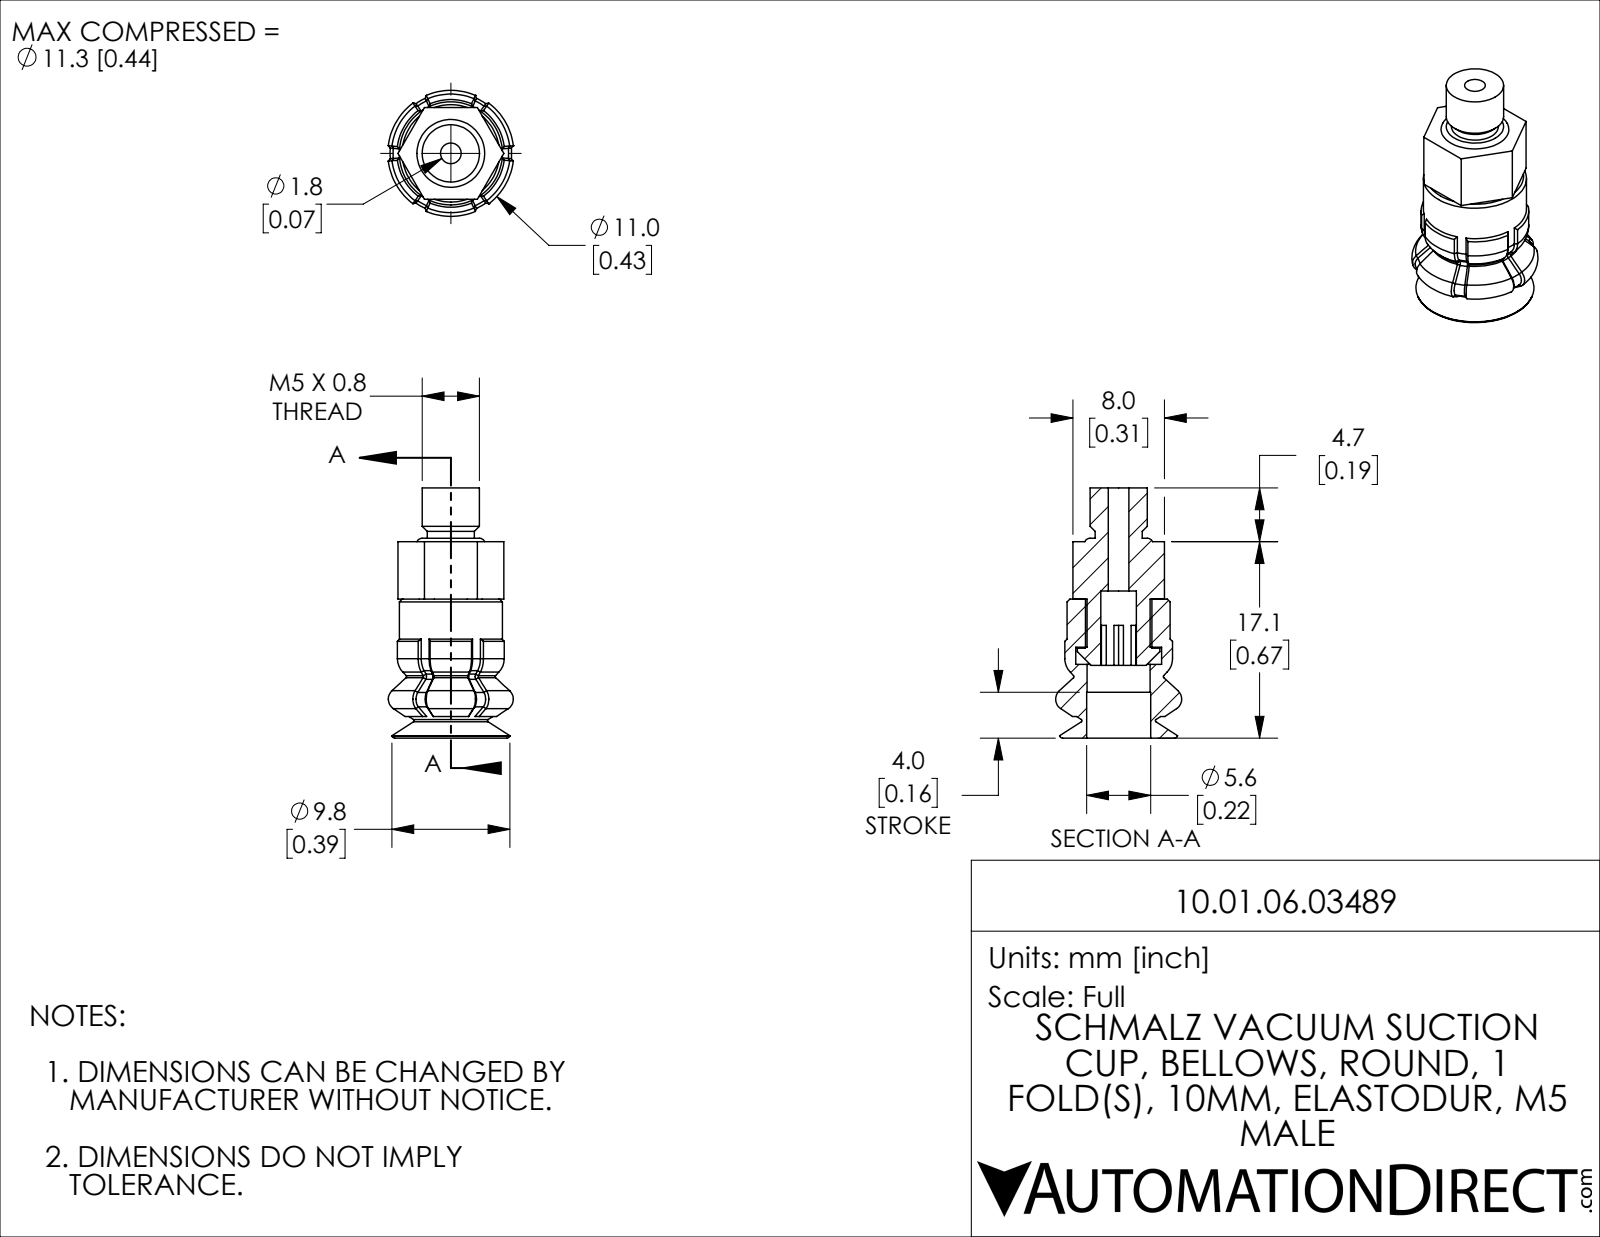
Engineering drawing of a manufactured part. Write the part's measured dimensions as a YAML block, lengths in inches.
part_name: "10.01.06.03489"
step_written_by: "SolidWorks 2021 (CONFIG_CONTROL_DESIGN)"
units: inches
bodies: {solids: 2, faces: 270, planar: 54, cylindrical: 34, other: 182}
overall_size: [0.86, 0.433, 0.43]
volume: 0.056
surface_area: 2.105
round_holes:
  - {diameter: 0.071, count: 1}
  - {diameter: 0.122, count: 1}
  - {diameter: 0.217, count: 1}
  - {diameter: 0.22, count: 1}
  - {diameter: 0.295, count: 1}
round_bosses_or_shafts:
  - {diameter: 0.354, count: 1}
  - {diameter: 0.283, count: 1}
  - {diameter: 0.228, count: 1}
  - {diameter: 0.197, count: 1}
  - {diameter: 0.161, count: 1}
partial_cylinders:
  - {radius: 11.507, count: 6}
  - {radius: 0.185, count: 1}
face_to_face_distances: [0.315, 0.478, 0.197, 0.059, 0.675, 0.254, 0.224, 0.421, 0.313, 0.165]
